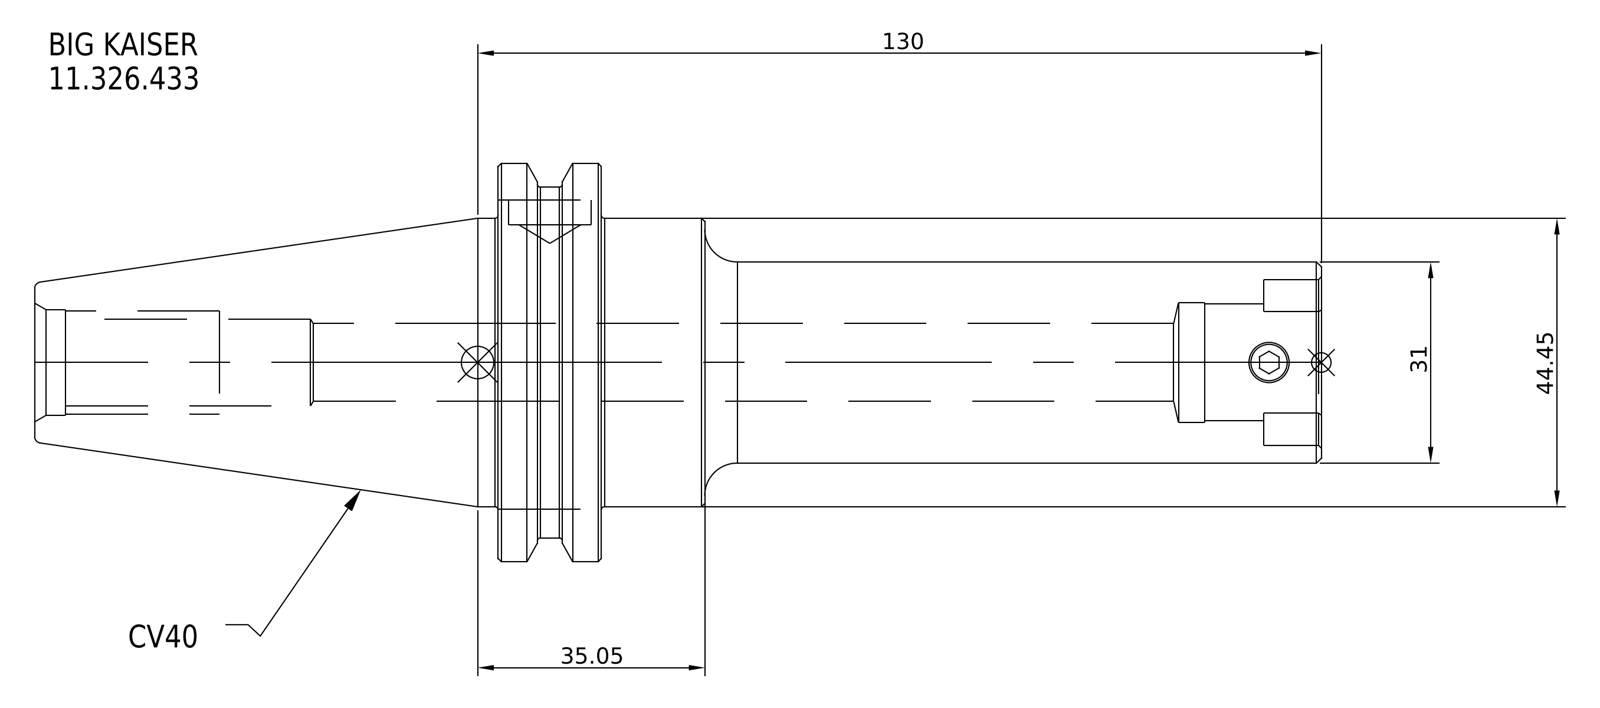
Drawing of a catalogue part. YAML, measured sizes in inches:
part_name: "11_326_433"
step_written_by: "SolidWorks 2021 (CONFIG_CONTROL_DESIGN)"
units: inches
bodies: {solids: 1, faces: 27, planar: 7, cylindrical: 12, other: 8}
overall_size: [7.805, 2.5, 2.5]
volume: 13.08
surface_area: 44.03
round_bosses_or_shafts:
  - {diameter: 2.5, count: 1}
  - {diameter: 2.219, count: 1}
  - {diameter: 1.75, count: 1}
  - {diameter: 1.22, count: 1}
face_to_face_distances: [0.625, 4.368, 4.993, 7.805, 3.437, 2.812, 3.738, 0.63, 1.255, 4.067]
